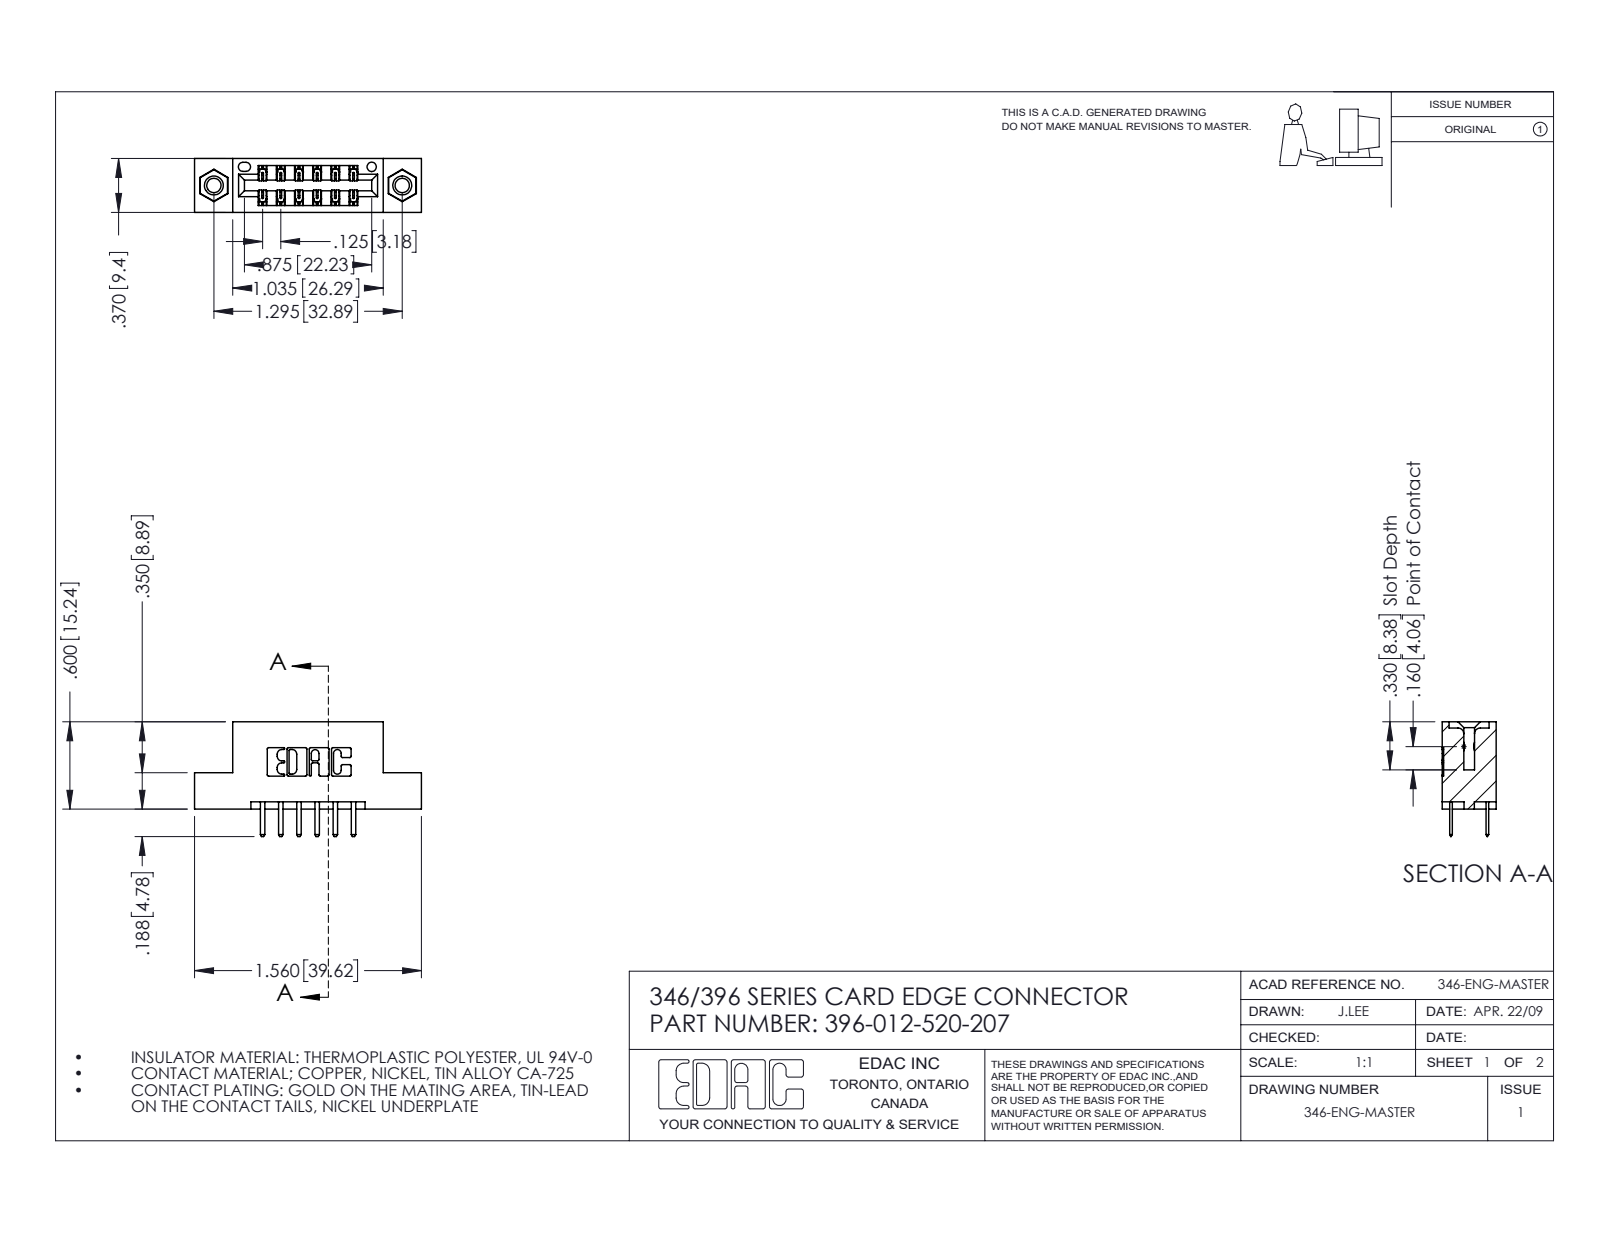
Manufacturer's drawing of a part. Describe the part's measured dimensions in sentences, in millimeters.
The part is named "346 Part_Flush Mounting Lugs - 0.156 Dia-TI; 345-292-001_345-293-120; 345-250-001_345-250-005-103; 396-012-520-207". Its 3-D file was written by "SolidWorks 2016 (CONFIG_CONTROL_DESIGN)". It is 15 solids with 854 faces: 552 planar, 286 cylindrical and 16 other. Overall it measures 39.6 by 20 by 9.4 millimeters. Its volume is 3 570 cubic millimeters and its surface area 4 357 square millimeters. Round holes: 2 of diameter 2.5, 2 of diameter 3.2, 2 of diameter 4, 1 of diameter 1.6. Round bosses or shafts: 2 of diameter 3.9. Partial cylindrical surfaces (rounded edges, fillets, slot ends): 22 of radius 0.3, 18 of radius 0.2, 16 of radius 0.3, 6 of radius 0.2, 6 of radius 0.8, 3 of radius 0.7, 2 of radius 0.4, 2 of radius 0.6. The main face-to-face distances are 6.4, 9.4, 1.2, 8.2, 3.8, 5.6, 2.5, 4.4, 3.2, 1.8. The hole center spacings are 6.2, 27.7, 32.9.
